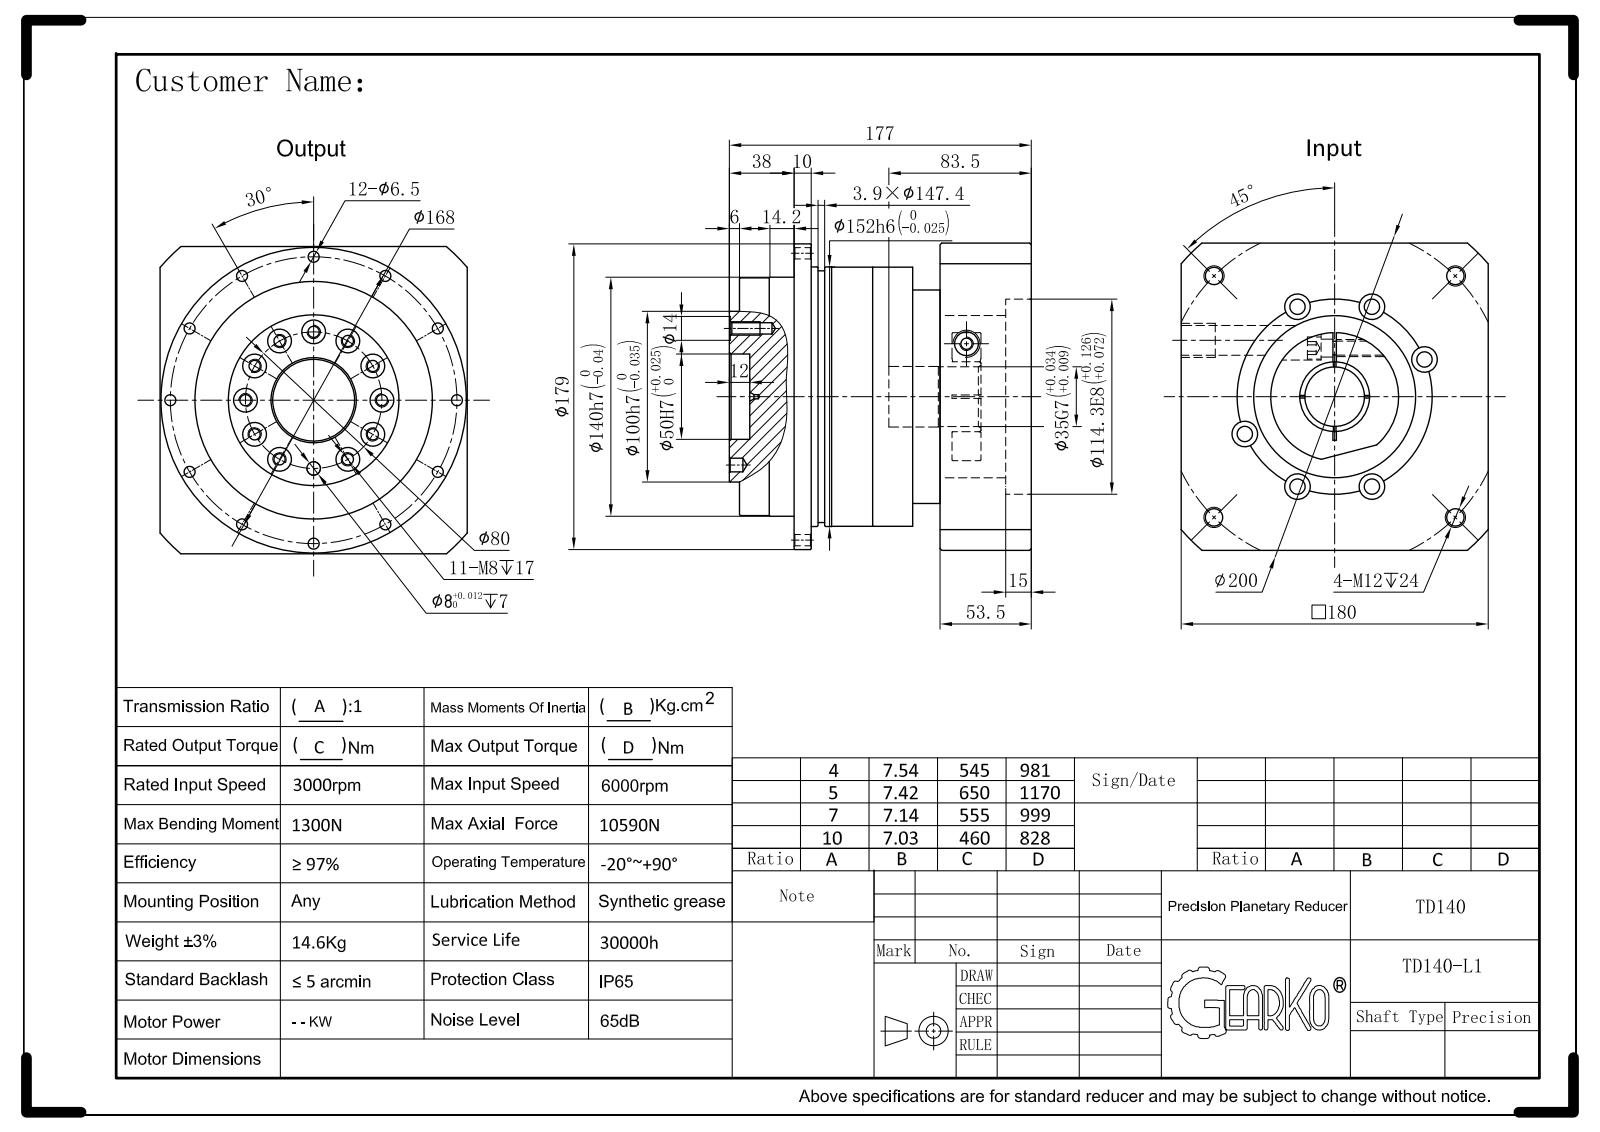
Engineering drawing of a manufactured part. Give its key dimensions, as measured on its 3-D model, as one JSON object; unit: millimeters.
{"part_name": "TD140-L1-35-114.3-200-M12-83.5-15", "step_written_by": "SolidWorks 2017 (CONFIG_CONTROL_DESIGN)", "units": "millimeters", "bodies": {"solids": 3, "faces": 303, "planar": 52, "cylindrical": 131, "other": 120}, "overall_size": [180, 180, 177], "volume_mm3": 3363000, "surface_area_mm2": 250646, "round_holes": [[6.6, 12], [6.8, 11], [14, 11], [10.2, 4], [2.5, 1], [8, 1], [17, 1], [17.5, 1], [35, 1], [41, 1], [50, 1], [50.5, 1]], "round_bosses_or_shafts": [[179, 1], [152, 1], [151.8, 1], [147.7, 1], [140, 1], [139.2, 1], [129, 1], [100, 1]], "partial_cylinders_radius": [[1, 1], [119, 1]], "face_to_face_distances": [53.5, 50.5, 180, 3, 85.5, 88.5, 139, 32, 117.5, 120.5], "hole_center_spacings": [84, 39.98, 120.31, 44.02, 72.81, 43.48, 72.74, 145.49]}
